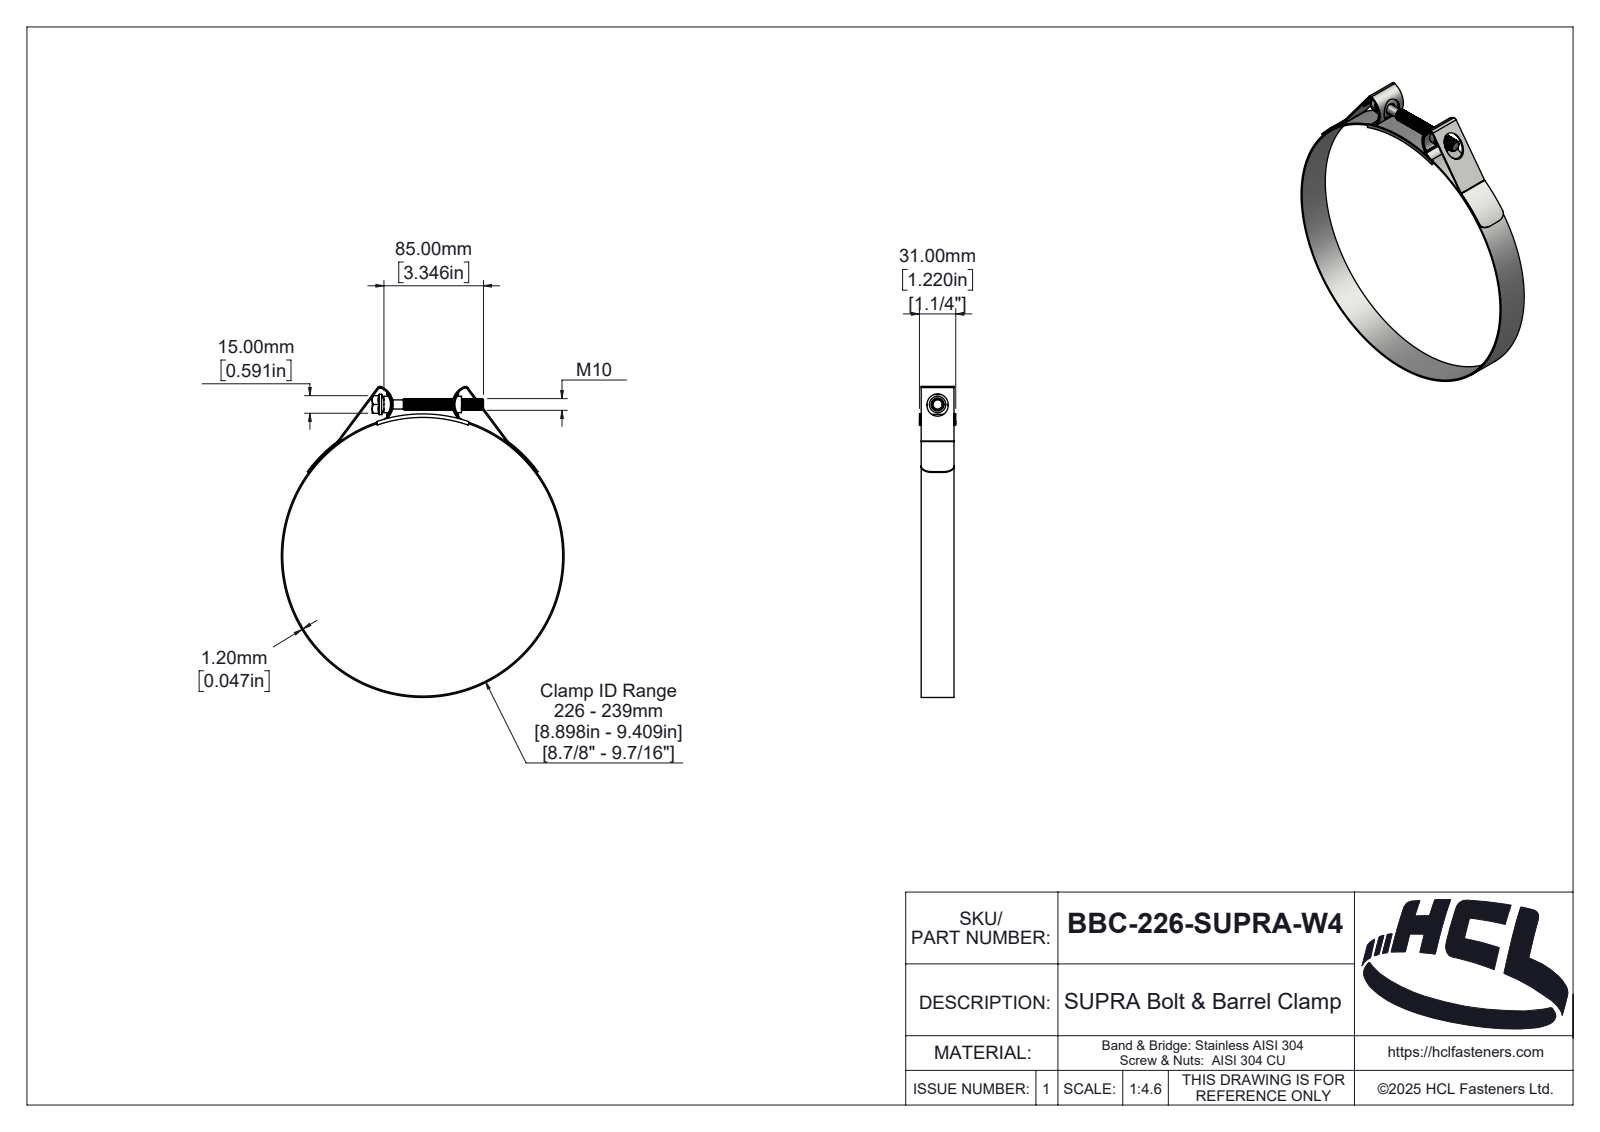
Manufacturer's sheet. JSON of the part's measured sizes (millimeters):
{"part_name": "BBC-226-SUPRA-W4", "step_written_by": "SolidWorks 2025 (AUTOMOTIVE_DESIGN)", "units": "millimeters", "bodies": {"solids": 5, "faces": 381, "planar": 50, "cylindrical": 245, "other": 86}, "overall_size": [265.48, 241.4, 31], "volume_mm3": 42938, "surface_area_mm2": 66667, "round_holes": [[239, 1]], "round_bosses_or_shafts": [[241.4, 1], [17.32, 1], [14, 1], [10, 1], [7.8, 1]], "partial_cylinders_radius": [[1, 4], [1.3, 2], [2, 2], [2.5, 2], [3.2, 2], [9, 2], [14.06, 2], [15.06, 2]], "face_to_face_distances": [1.2, 28, 1.5, 29.5, 29.8, 28.3, 31, 28.6, 15, 2.5]}
